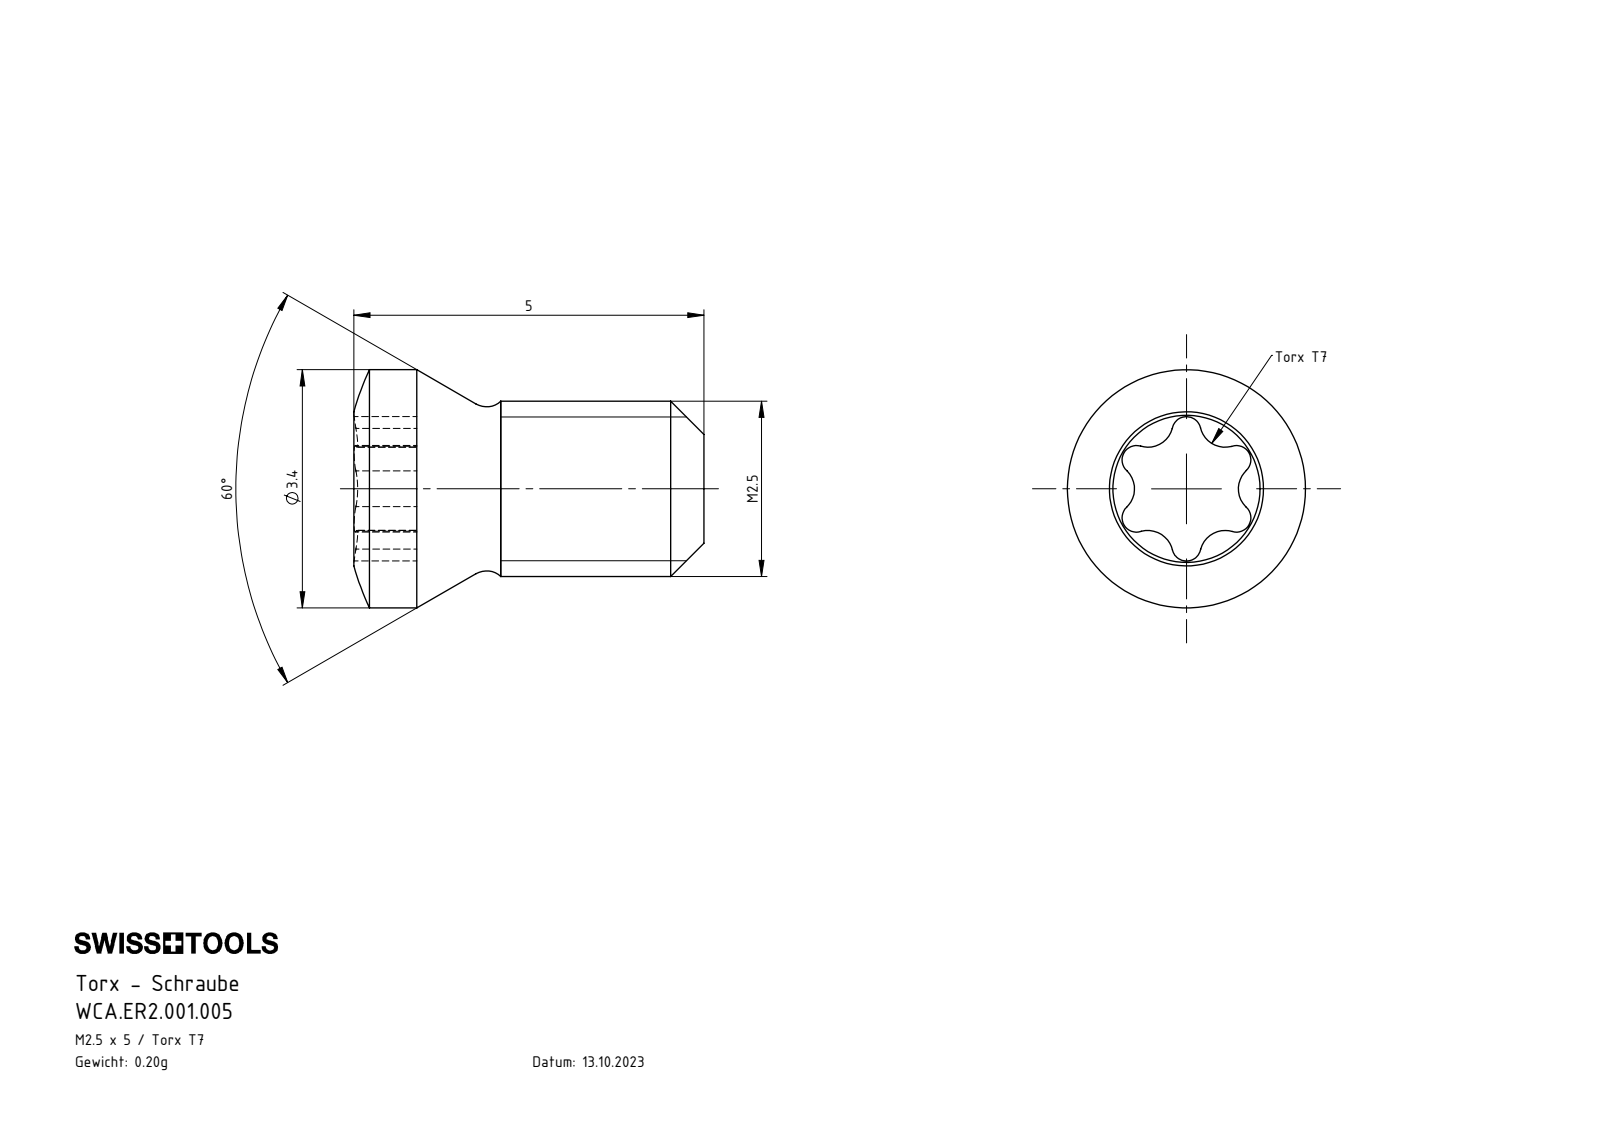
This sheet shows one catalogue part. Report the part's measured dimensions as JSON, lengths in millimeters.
{"part_name": "WCA.ER2.001.005", "step_written_by": "SolidWorks 2017 (AUTOMOTIVE_DESIGN)", "units": "millimeters", "bodies": {"solids": 1, "faces": 34, "planar": 3, "cylindrical": 19, "other": 12}, "overall_size": [5, 3.4, 3.4], "volume_mm3": 26, "surface_area_mm2": 60, "round_bosses_or_shafts": [[3.4, 1], [2.5, 1]], "partial_cylinders_radius": [[0.21, 6], [0.36, 5], [0.36, 1]], "face_to_face_distances": [4.1, 0.9, 5]}
